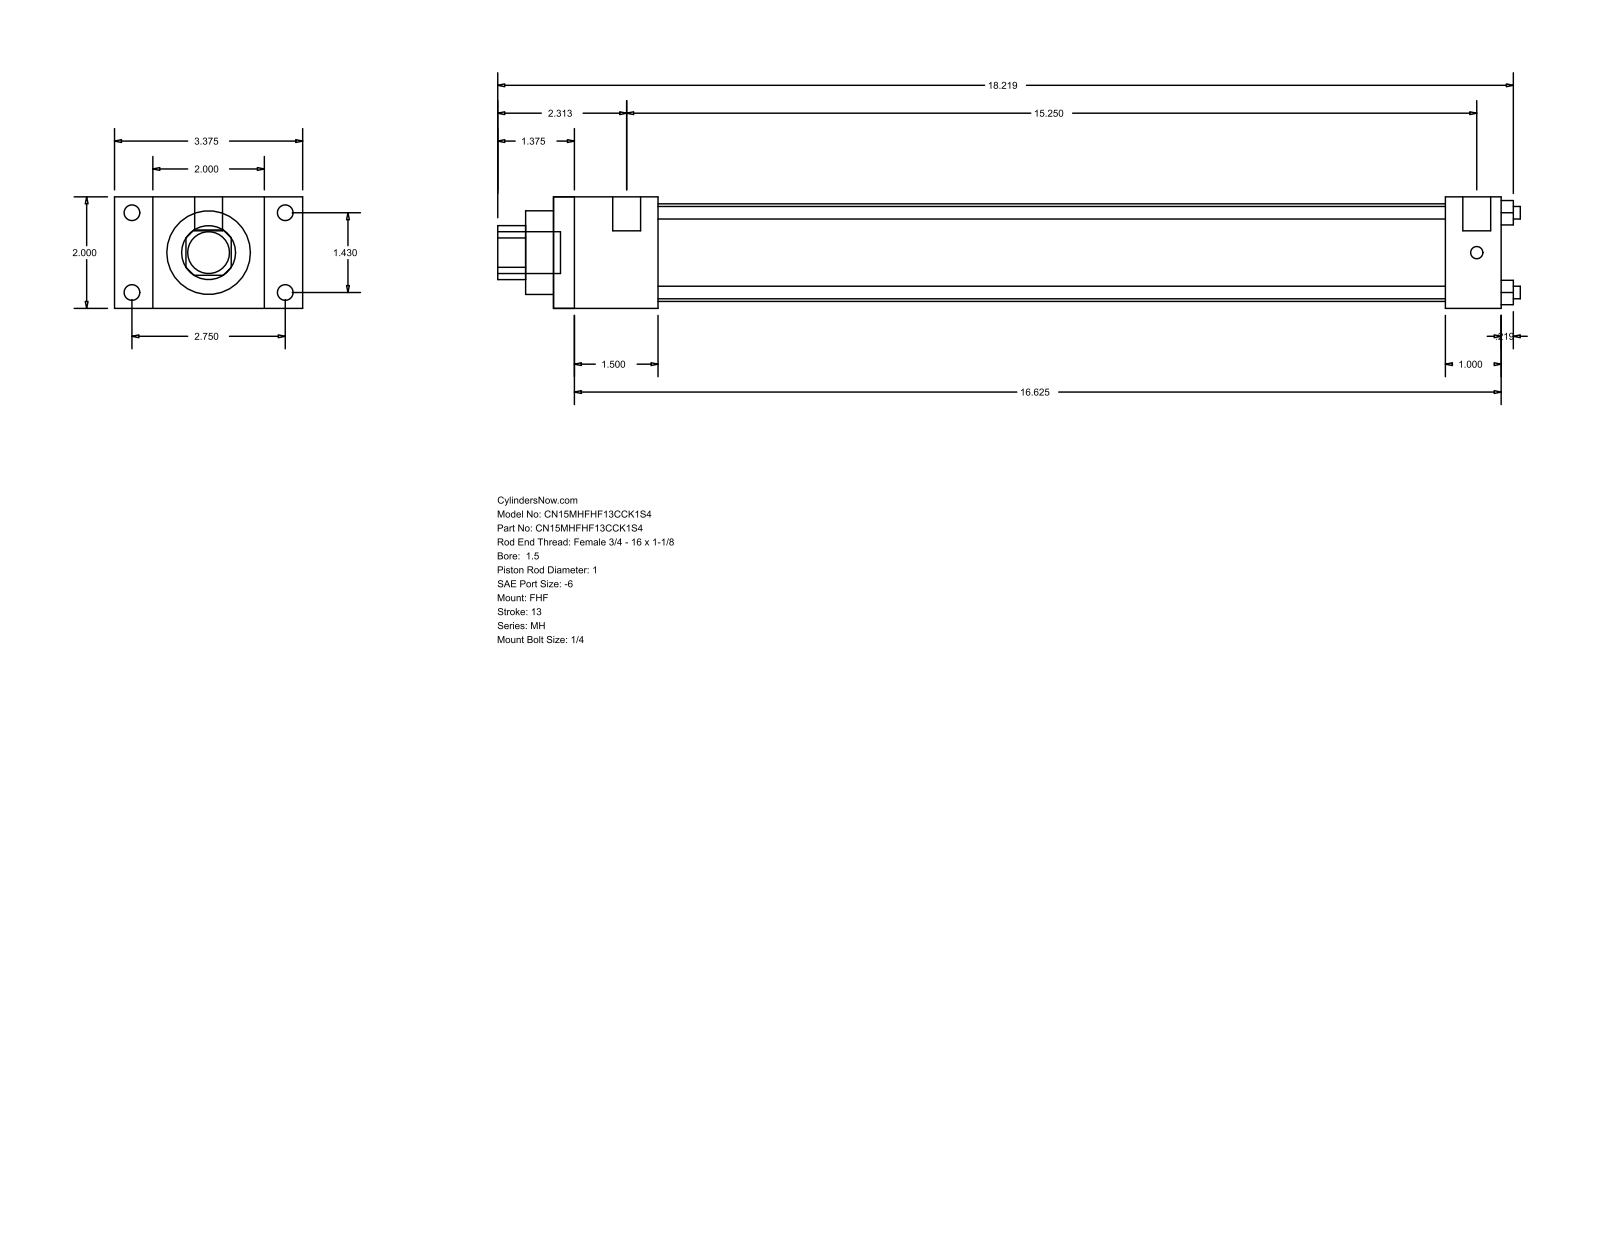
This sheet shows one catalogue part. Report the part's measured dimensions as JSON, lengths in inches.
{"part_name": "MH_FHF__0150_1", "step_written_by": "GSSL Pune (CONFIG_CONTROL_DESIGN)", "units": "inches", "bodies": {"solids": 0, "faces": 88, "planar": 60, "cylindrical": 28, "other": 0}, "overall_size": [18.344, 3.375, 2], "round_holes": [[0.225, 4], [1, 1], [1.5, 1], [1.75, 1]], "round_bosses_or_shafts": [[0.281, 4], [0.219, 4], [0.5, 2], [0.75, 1]], "partial_cylinders_radius": [[0.484, 1]], "face_to_face_distances": [2, 0.687, 2.687, 1.875, 3.375, 17, 15.125, 1, 16, 14.125], "hole_center_spacings": [1.011, 1.43, 2.022]}
